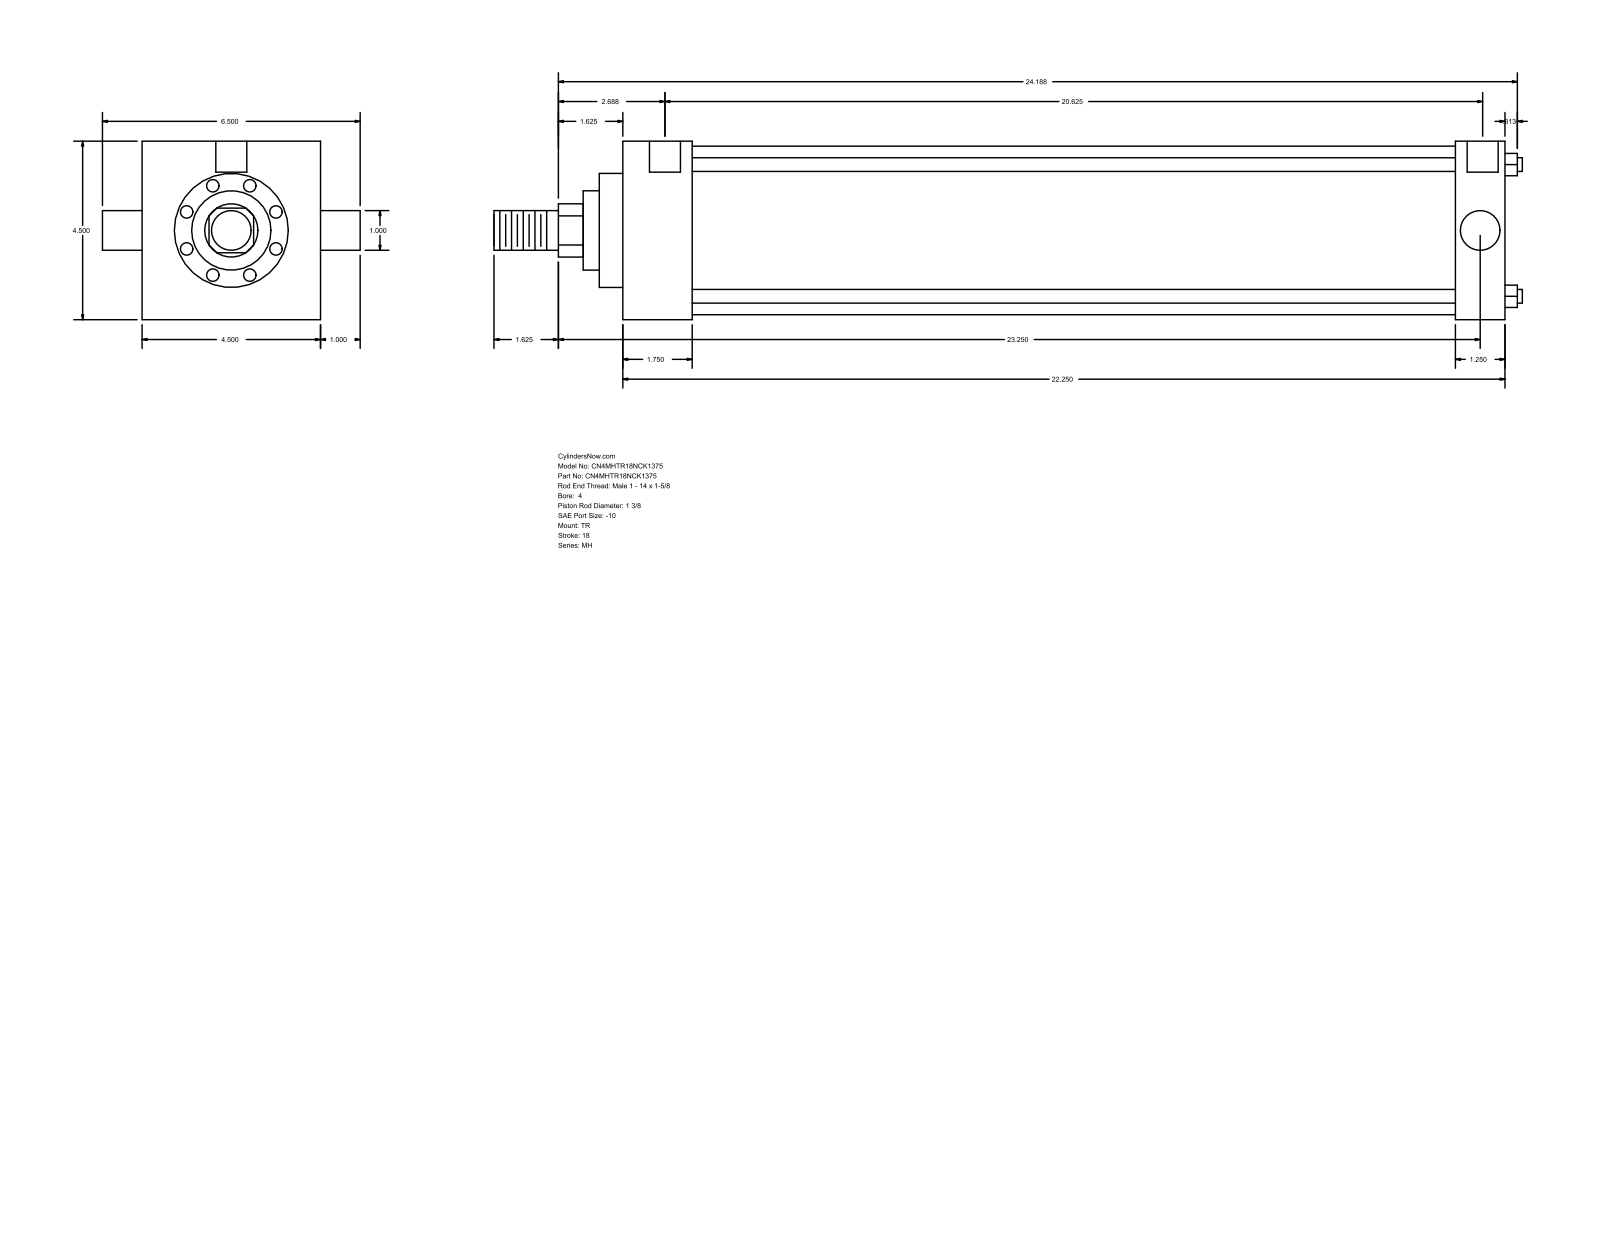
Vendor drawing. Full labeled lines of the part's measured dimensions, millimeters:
Part name (STEP PRODUCT): MH_TR__0400_1.375
STEP written by: GSSL Pune (CONFIG_CONTROL_DESIGN)
Units: millimetres
Bodies: 0 solids, 86 faces (61 planar, 25 cylindrical, 0 other)
Overall size (bounding box): 658.81 × 165.1 × 114.3
Round holes (diameter × count): ⌀8.73 ×3, ⌀19.84 ×2
Round bosses / shafts (diameter × count): ⌀8.76 ×4, ⌀25.4 ×2, ⌀107.95 ×1, ⌀73.03 ×1, ⌀50.8 ×1, ⌀34.92 ×1
Partial cylindrical surfaces — rounded edges, fillets, slot ends (radius × count): R17.06 ×1
Main face-to-face distances: 114.3, 565.15, 44.45, 520.7, 533.4, 488.95, 31.75, 15.08, 59.53, 548.48
Hole centre spacings: 1.59, 525.47, 523.88, 527.06
